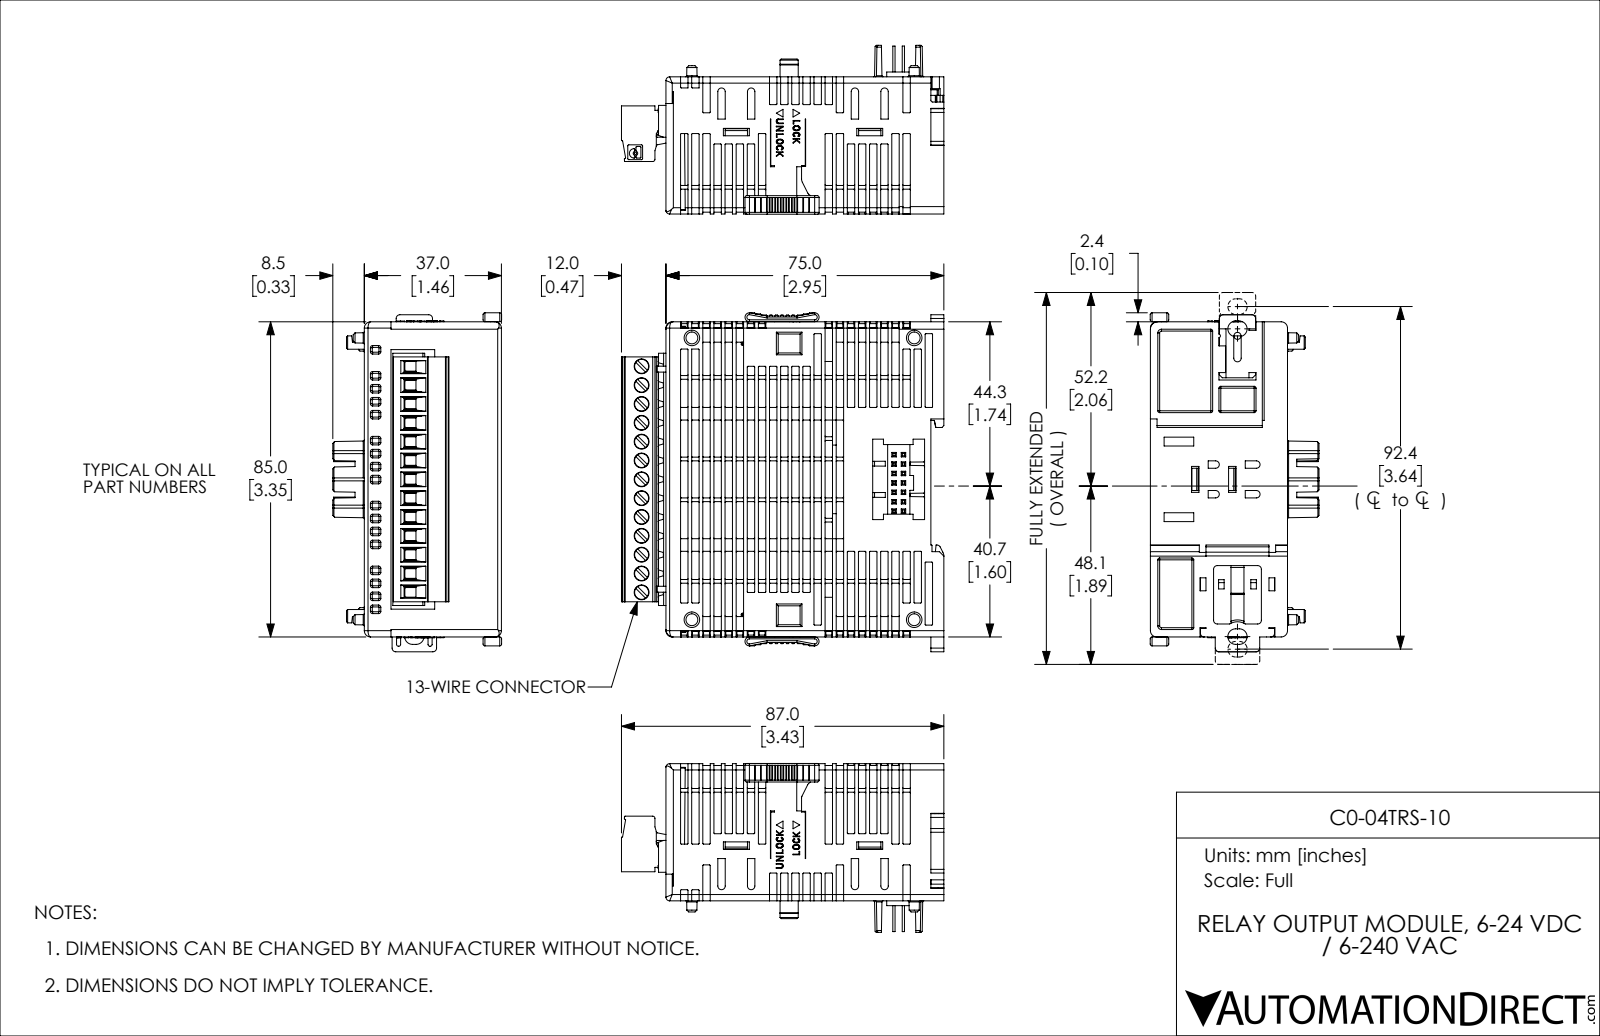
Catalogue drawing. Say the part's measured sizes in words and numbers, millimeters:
The part is named "C0-04TRS-10". Its 3-D file was written by "SolidWorks 2019 (AUTOMOTIVE_DESIGN)". It is 1 solid with 4458 faces: 3231 planar, 1113 cylindrical and 114 other. Overall it measures 91.4 by 87 by 45.5 millimeters. Its volume is 230 100 cubic millimeters and its surface area 41 830 square millimeters. Round holes: 13 of diameter 4, 4 of diameter 3.2. Round bosses or shafts: 13 of diameter 3.8, 1 of diameter 1.9, 1 of diameter 0.6. Partial cylindrical surfaces (rounded edges, fillets, slot ends): 654 of radius 0.2, 69 of radius 0.1, 56 of radius 0.3, 47 of radius 0.5, 26 of radius 1, 13 of radius 2.9, 10 of radius 0.2, 6 of radius 1.7. The main face-to-face distances are 37, 1.7, 35.3, 71.5, 85, 3, 1.5, 83.5, 2, 1. The hole center spacings are 5.1, 10.2, 15.2, 20.3, 25.4, 30.5, 35.6, 40.6.
